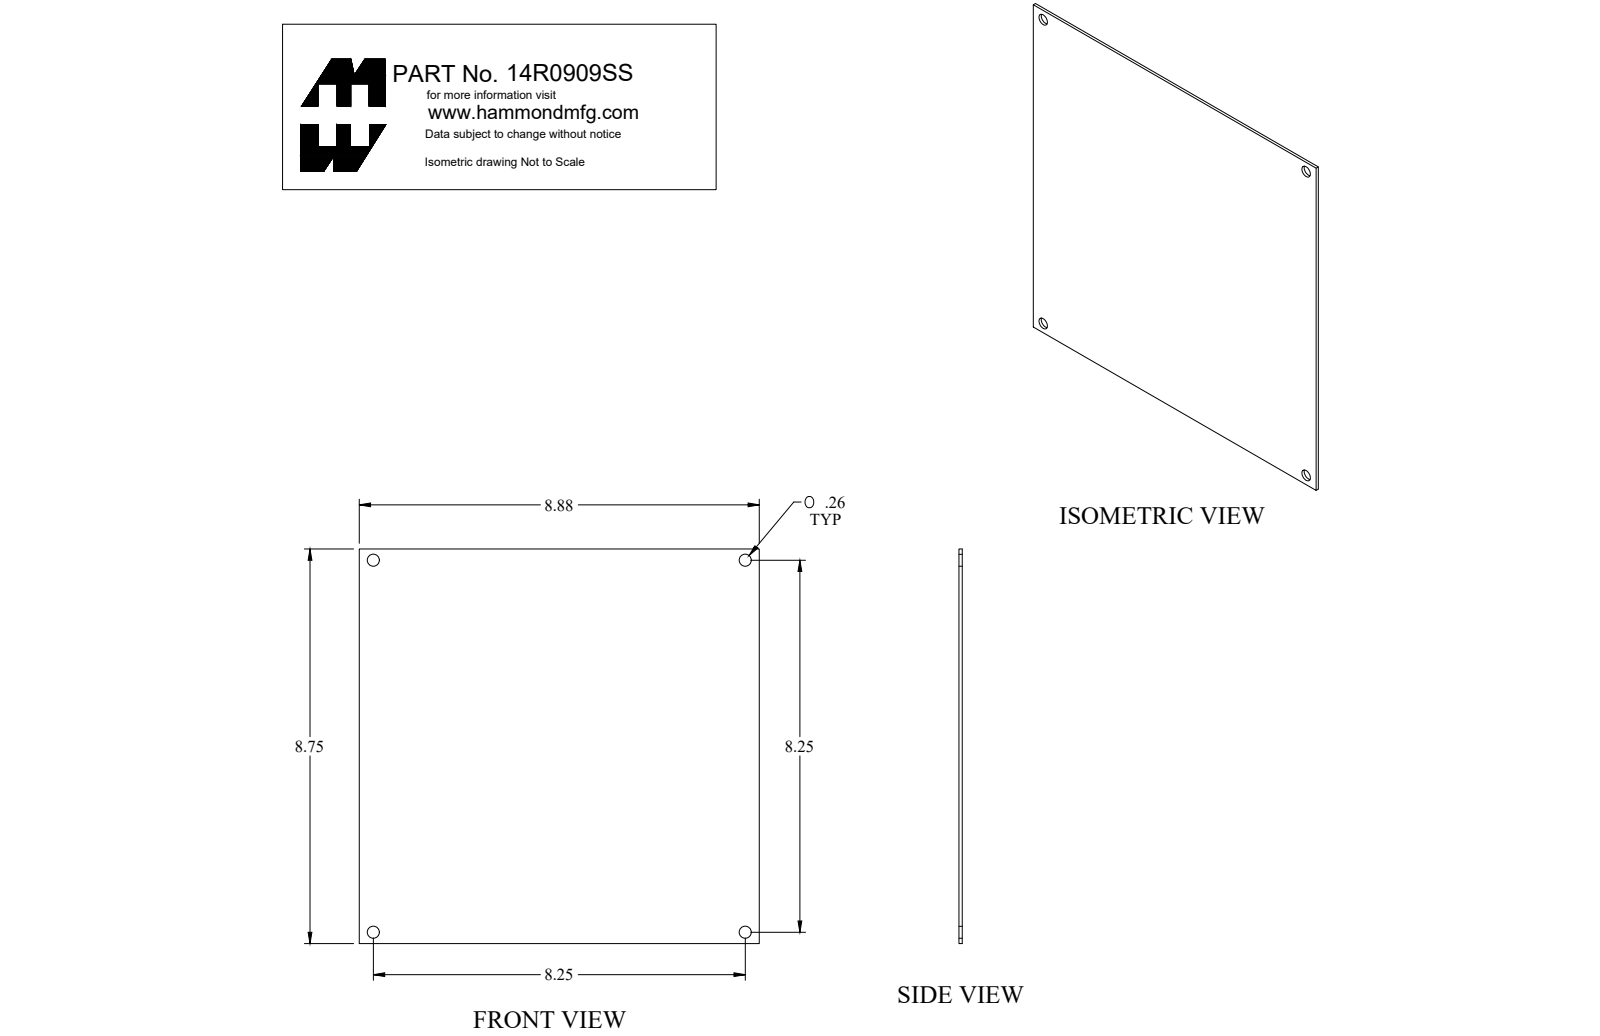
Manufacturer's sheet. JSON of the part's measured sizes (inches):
{"part_name": "14R0909SS", "step_written_by": "SolidWorks 2018 (AUTOMOTIVE_DESIGN)", "units": "inches", "bodies": {"solids": 1, "faces": 10, "planar": 6, "cylindrical": 4, "other": 0}, "overall_size": [8.875, 8.75, 0.072], "volume_in3": 5.575, "surface_area_in2": 157.6, "round_holes": [[0.265, 4]], "face_to_face_distances": [0.072, 8.75, 8.875], "hole_center_spacings": [8.25, 11.667]}
